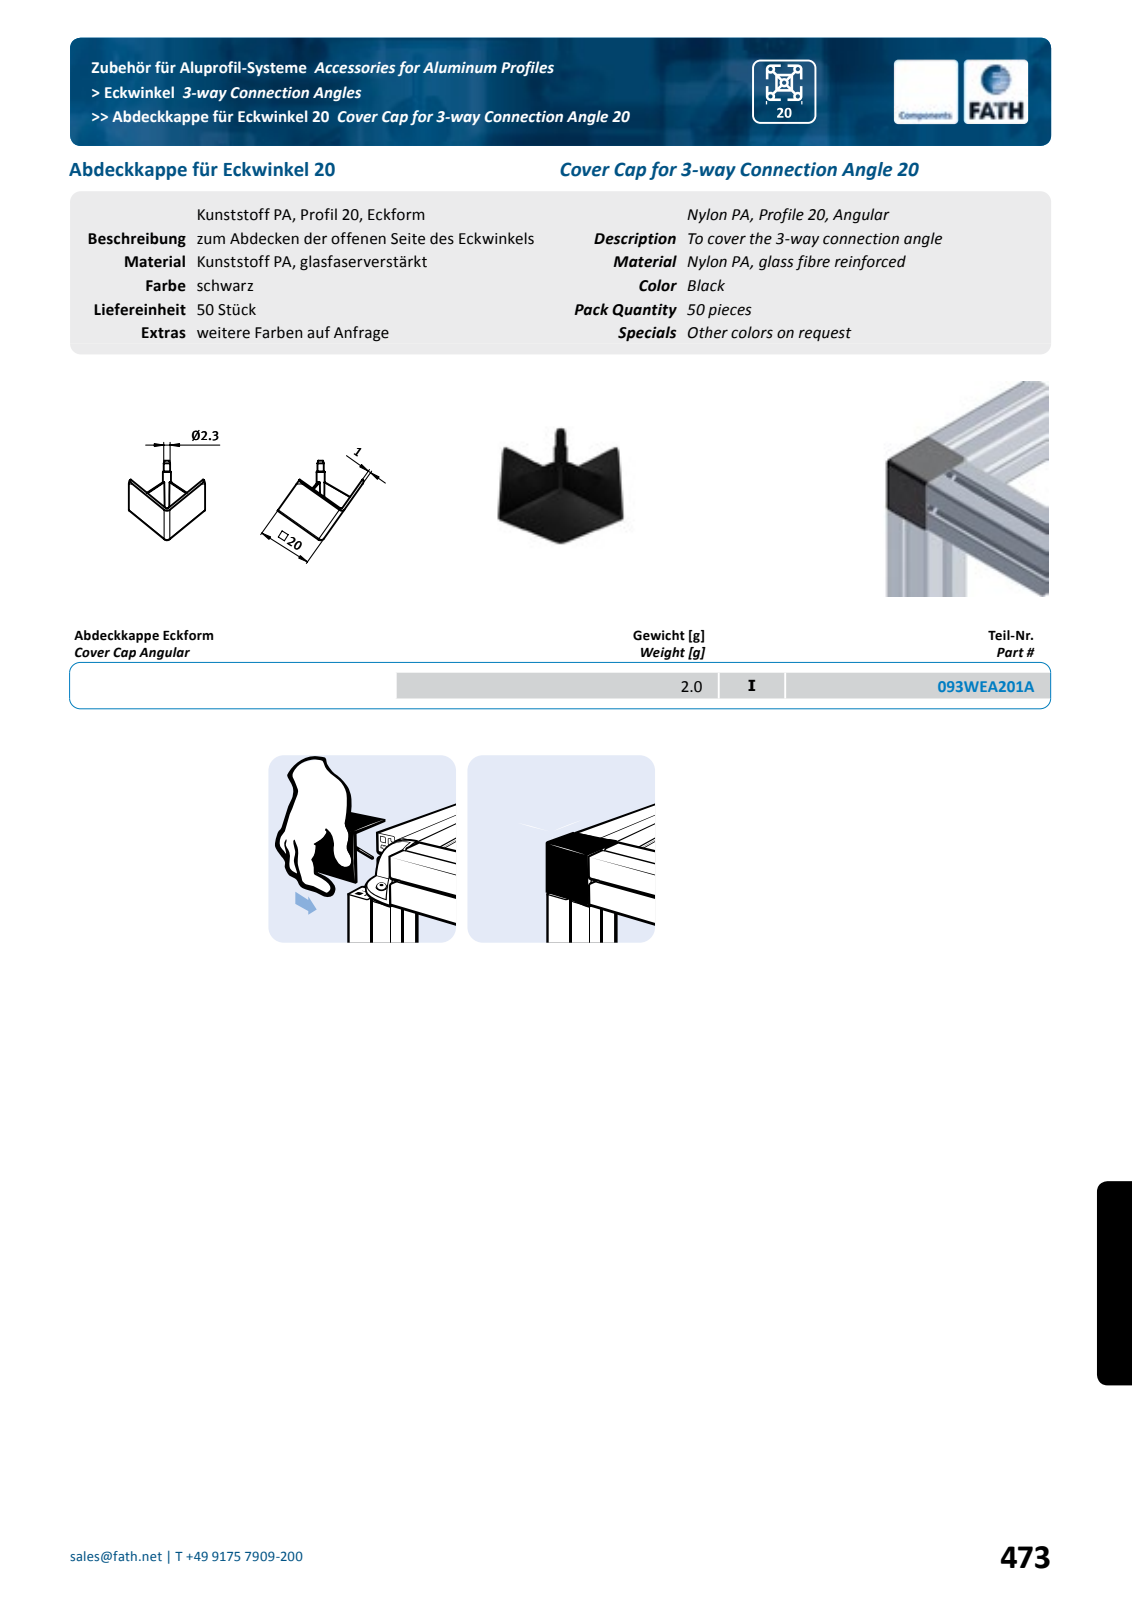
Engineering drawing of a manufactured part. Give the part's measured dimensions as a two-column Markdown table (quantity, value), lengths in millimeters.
| quantity | value |
| --- | --- |
| part name | fath_093wea201a |
| STEP written by | Spatial InterOp 3D (automotive_design) |
| units | millimeters |
| bodies | 1 solid, 47 faces (20 planar, 22 cylindrical, 5 other) |
| overall size | 20 × 20 × 20 |
| volume | 1 620 mm³ |
| surface area | 3 025 mm² |
| round bosses / shafts (diameter × count) | 3 × 1, 2.35 × 1 |
| partial cylindrical surfaces (radius × count) | 0.2 × 6, 0.5 × 3, 1.5 × 3, 2 × 3 |
| main face-to-face distances | 1, 20, 19, 3.99 |
